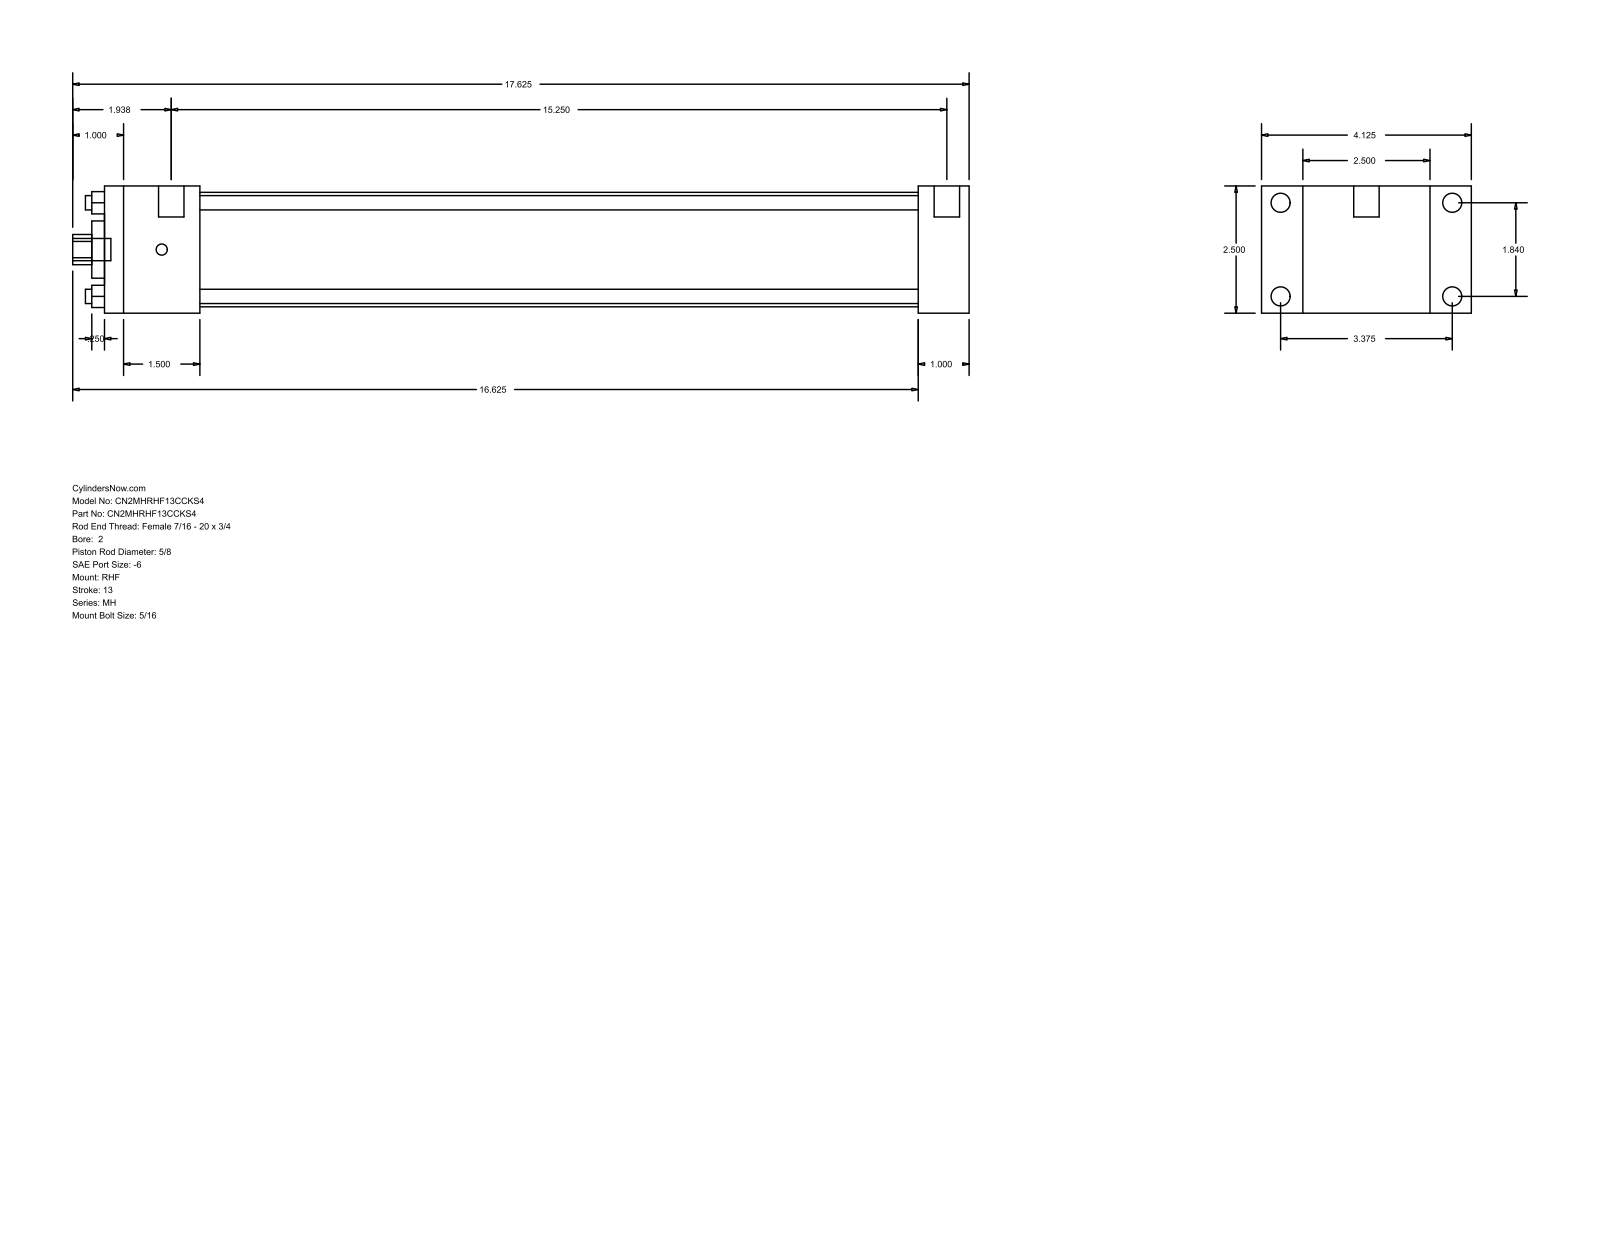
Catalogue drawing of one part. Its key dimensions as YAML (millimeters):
part_name: "MH_RHF__0200_0.625"
step_written_by: "GSSL Pune (CONFIG_CONTROL_DESIGN)"
units: millimeters
bodies: {solids: 0, faces: 88, planar: 60, cylindrical: 28, other: 0}
overall_size: [447.68, 104.78, 63.5]
round_holes:
  - {diameter: 7.14, count: 4}
  - {diameter: 15.88, count: 1}
  - {diameter: 28.57, count: 1}
  - {diameter: 57.15, count: 1}
round_bosses_or_shafts:
  - {diameter: 9.53, count: 4}
  - {diameter: 5.56, count: 4}
  - {diameter: 12.7, count: 2}
  - {diameter: 11.11, count: 1}
partial_cylinders:
  - {radius: 7.54, count: 1}
face_to_face_distances: [63.5, 25.41, 20.64, 84.14, 406.39, 431.8, 104.78, 47.62, 358.77, 384.18]
hole_center_spacings: [33.05, 46.74, 66.1]
